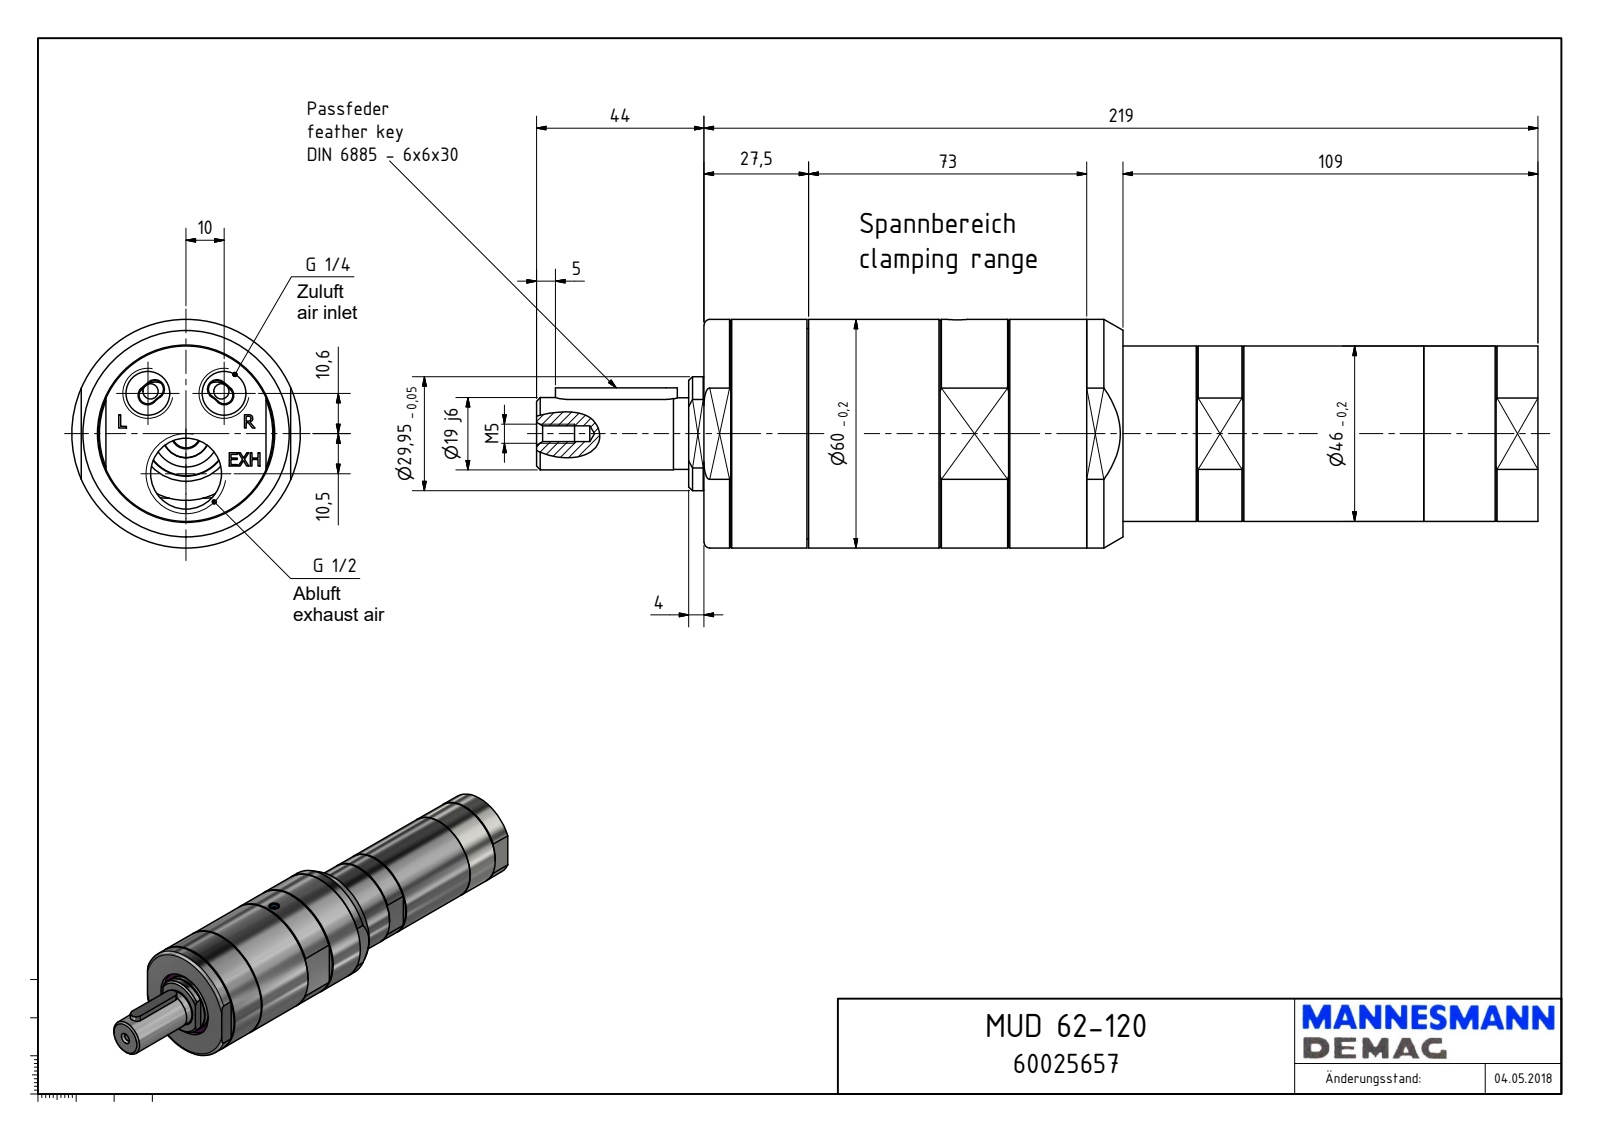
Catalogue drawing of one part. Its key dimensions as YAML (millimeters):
part_name: "MUD 62-120_60025657"
step_written_by: "Autodesk Inventor 2018 (AUTOMOTIVE_DESIGN)"
units: millimeters
bodies: {solids: 1, faces: 224, planar: 119, cylindrical: 49, other: 56}
overall_size: [263, 60, 60]
volume: 494535
surface_area: 54302
round_holes:
  - {diameter: 11.45, count: 2}
  - {diameter: 1.55, count: 1}
  - {diameter: 4, count: 1}
  - {diameter: 4.13, count: 1}
  - {diameter: 5.5, count: 1}
  - {diameter: 18.63, count: 1}
  - {diameter: 35, count: 1}
  - {diameter: 36.5, count: 1}
  - {diameter: 46.5, count: 1}
  - {diameter: 55.38, count: 1}
round_bosses_or_shafts:
  - {diameter: 60, count: 1}
  - {diameter: 55.18, count: 1}
  - {diameter: 46, count: 1}
  - {diameter: 40, count: 1}
  - {diameter: 33.71, count: 1}
  - {diameter: 29.95, count: 1}
  - {diameter: 19, count: 1}
  - {diameter: 18.8, count: 1}
partial_cylinders:
  - {radius: 3, count: 2}
  - {radius: 5, count: 2}
  - {radius: 19, count: 1}
  - {radius: 25.5, count: 1}
face_to_face_distances: [6.5, 219, 48.5, 55, 0.5, 76, 107.5, 110, 109, 103]
hole_center_spacings: [14.57, 23.35, 10.5, 20]
